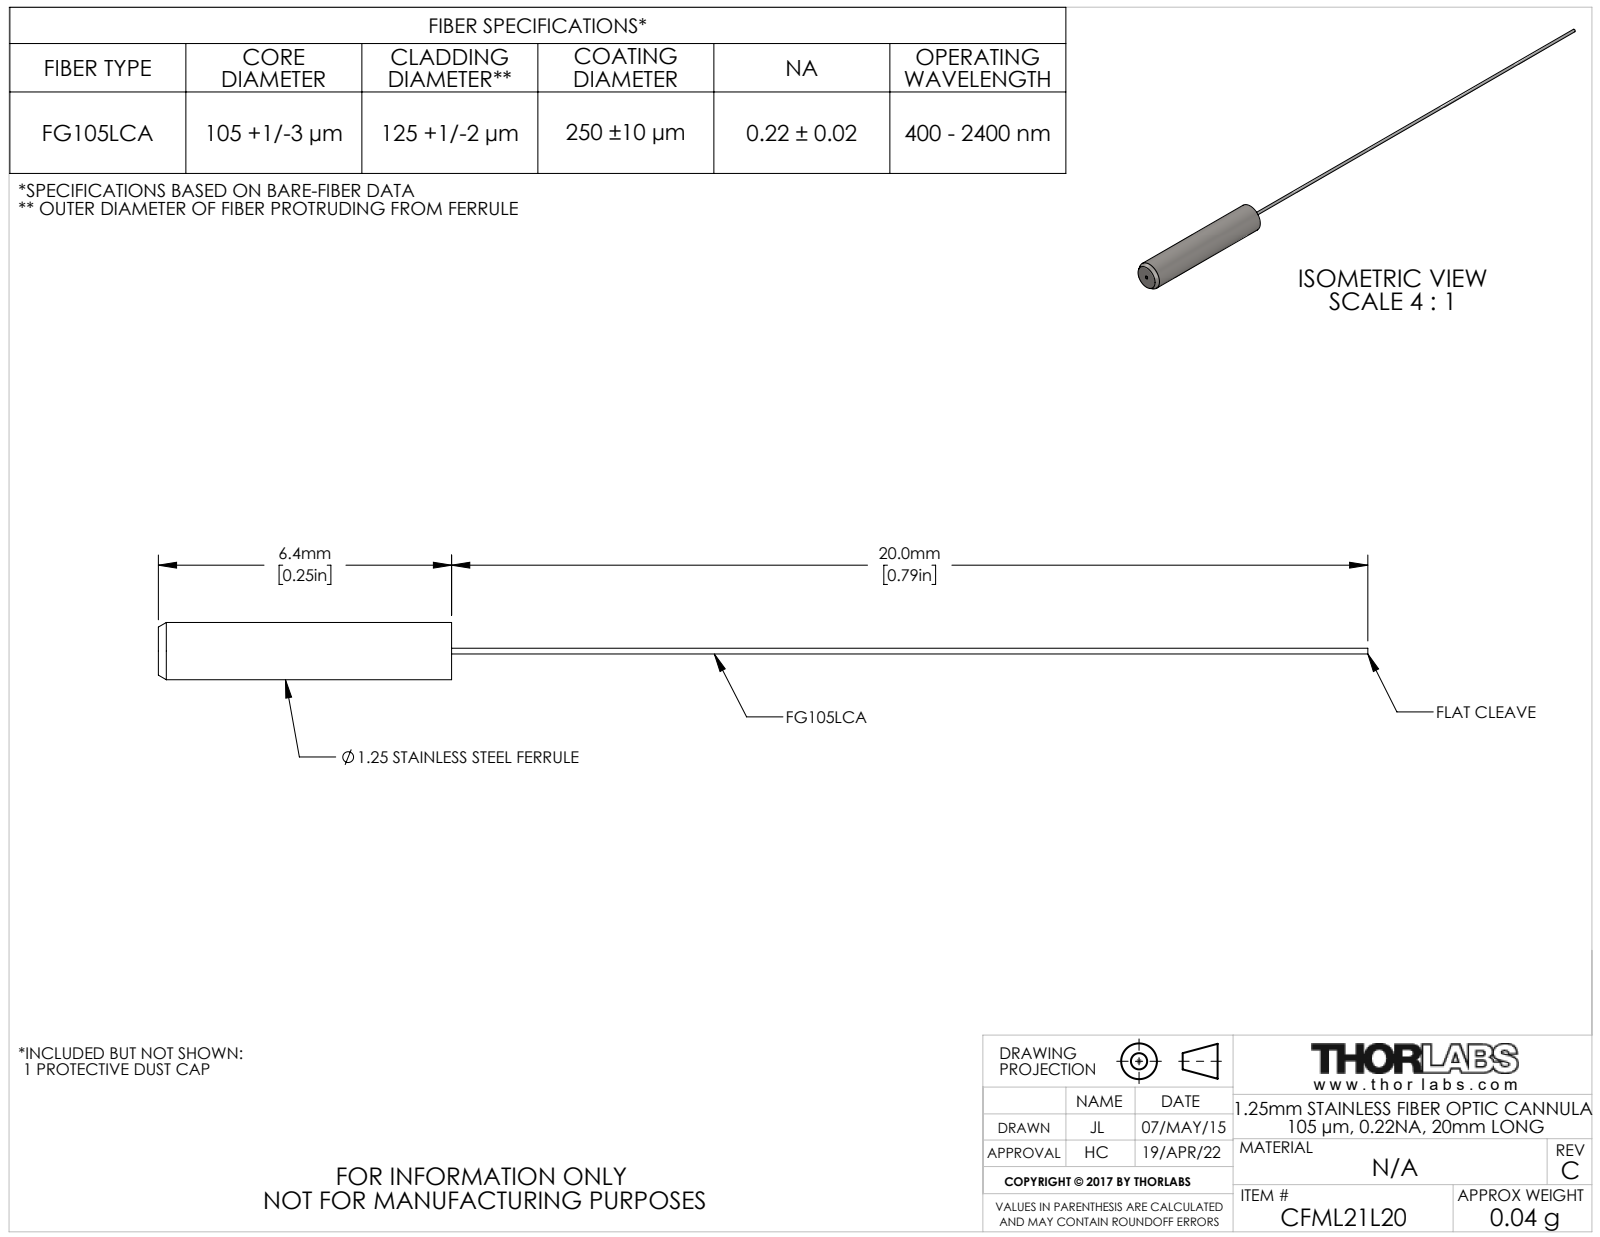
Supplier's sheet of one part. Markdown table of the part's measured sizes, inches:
| quantity | value |
| --- | --- |
| part name | TTN041714-E0W |
| STEP written by | SolidWorks 2014 (CONFIG_CONTROL_DESIGN) |
| units | inches |
| bodies | 2 solids, 18 faces (4 planar, 8 cylindrical, 6 other) |
| overall size | 1.039 × 0.049 × 0.049 |
| round holes (diameter × count) | 0.039 × 1 |
| round bosses / shafts (diameter × count) | 0.049 × 1 |
| main face-to-face distances | 0.252, 1.039, 0.787 |
